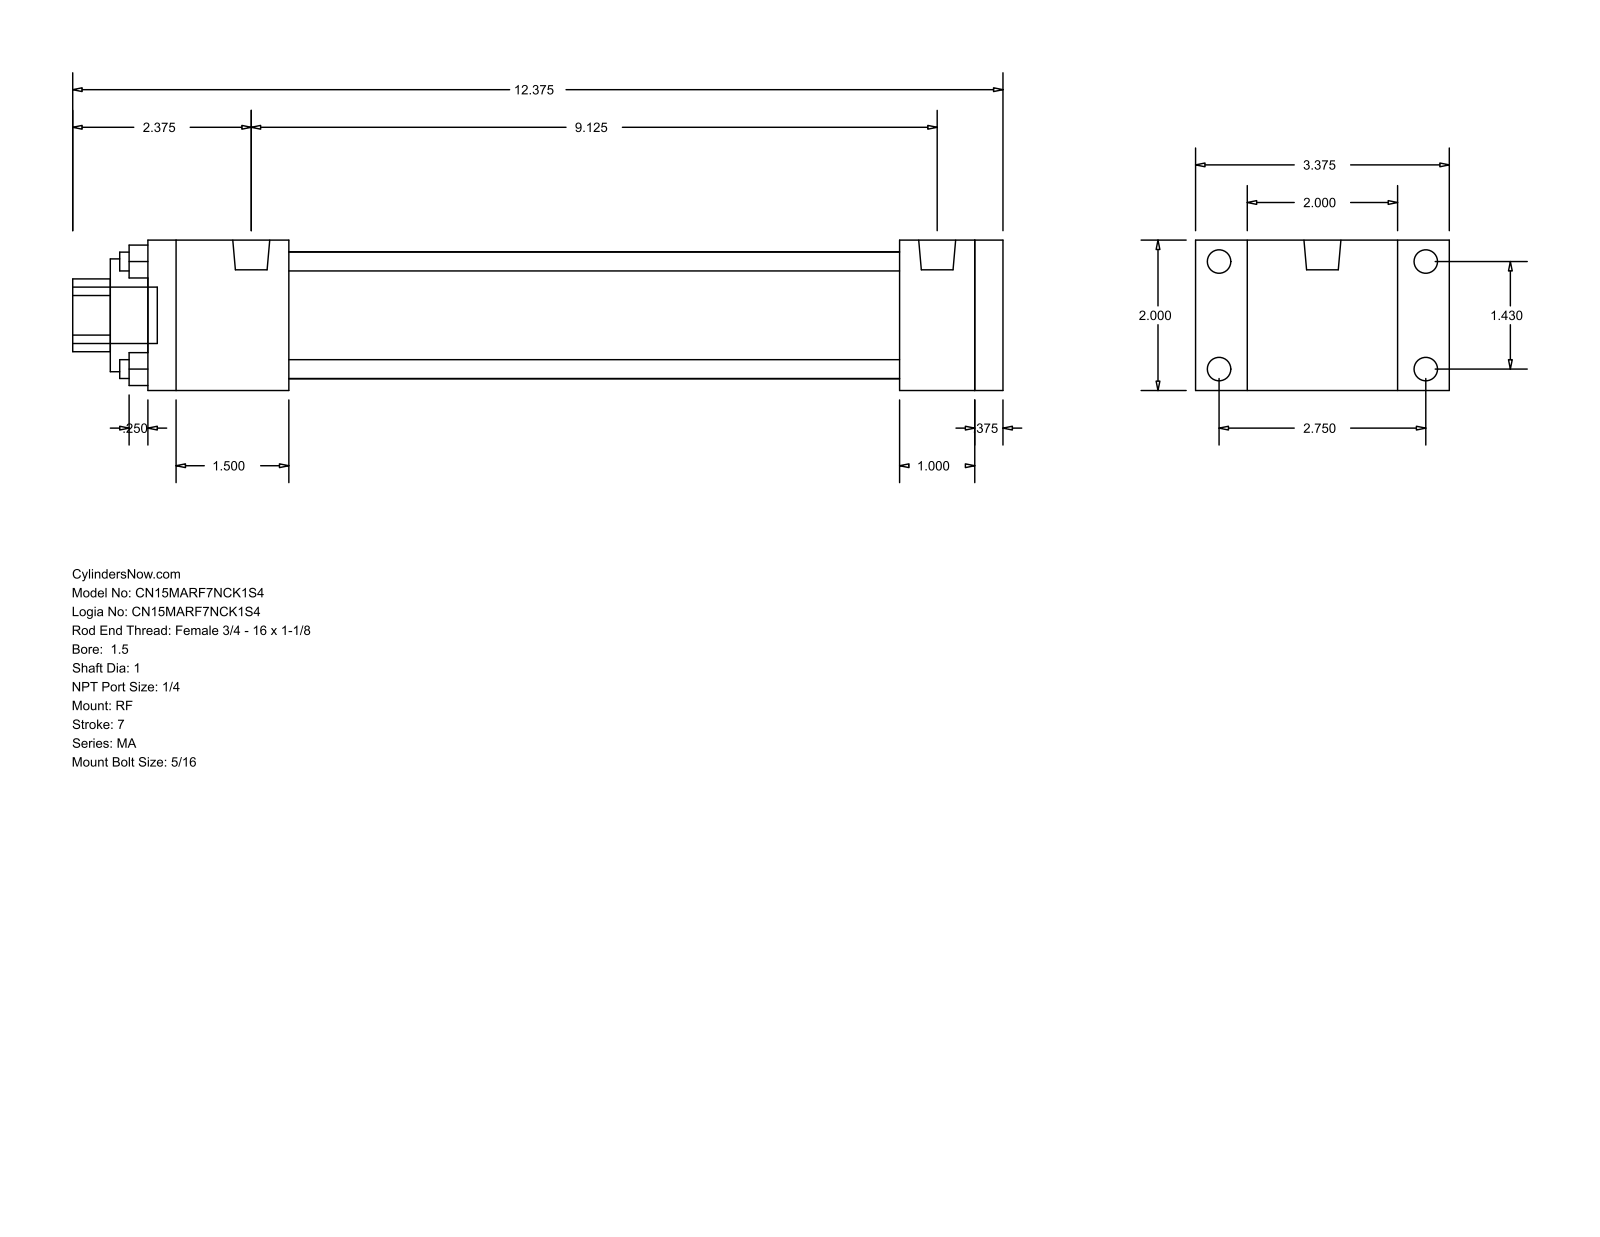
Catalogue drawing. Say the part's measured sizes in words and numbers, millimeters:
The part is named "MA_RF__0150_1". Its 3-D file was written by "GSSL Pune (CONFIG_CONTROL_DESIGN)". It is 0 solids with 92 faces: 64 planar, 28 cylindrical and 0 other. Overall it measures 314.32 by 85.72 by 50.8 millimeters. Round holes: 4 of diameter 6.35, 1 of diameter 25.4, 1 of diameter 38.1, 1 of diameter 42.93. Round bosses or shafts: 8 of diameter 7.94, 2 of diameter 12.49, 1 of diameter 19.05. Partial cylindrical surfaces (rounded edges, fillets, slot ends): 1 of radius 12.29. The main face-to-face distances are 50.8, 9.52, 288.92, 279.4, 25.4, 254, 34.92, 47.63, 206.37, 231.77. The hole center spacings are 25.68, 36.32, 51.36.
